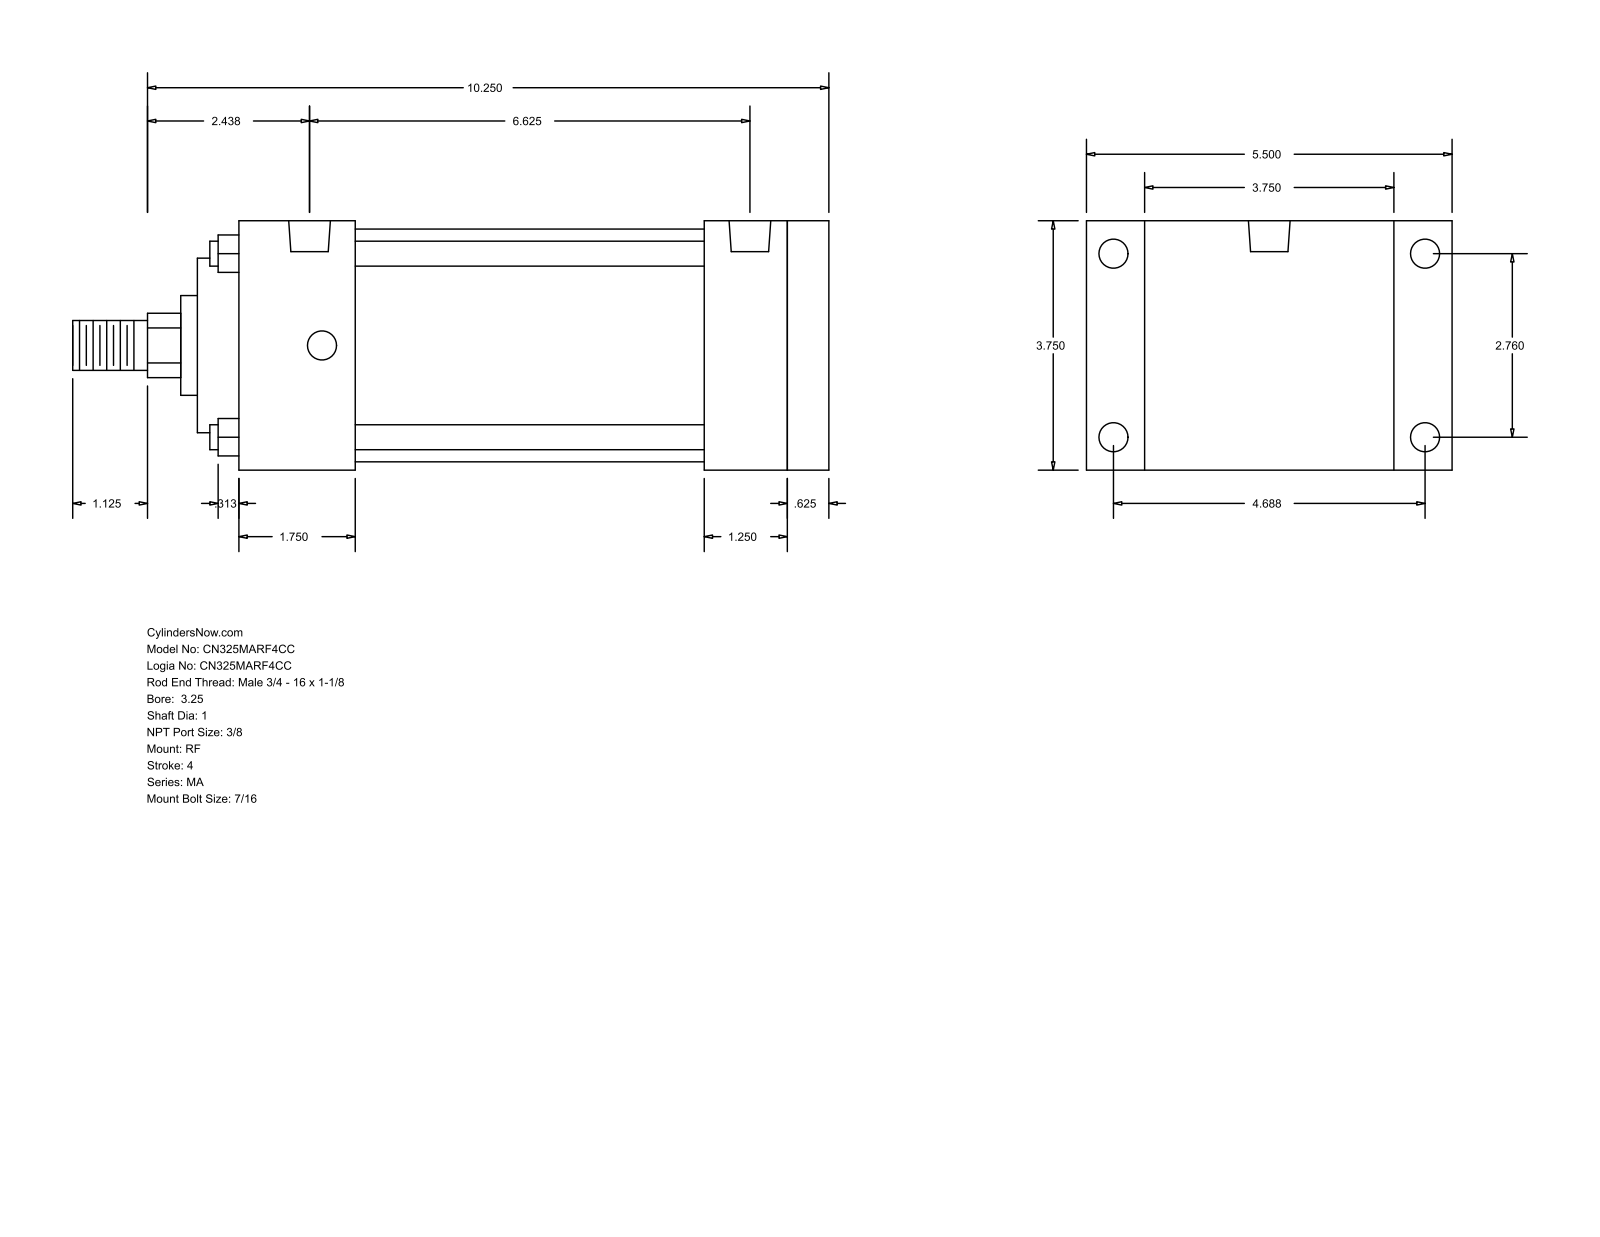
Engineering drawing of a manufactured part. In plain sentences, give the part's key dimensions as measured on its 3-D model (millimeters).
The part is named "MA_RF__0325_1". Its 3-D file was written by "GSSL Pune (CONFIG_CONTROL_DESIGN)". It is 0 solids with 94 faces: 65 planar, 29 cylindrical and 0 other. Overall it measures 288.93 by 139.7 by 95.25 millimeters. Round holes: 8 of diameter 11.11, 2 of diameter 15.93. Round bosses or shafts: 4 of diameter 9.53, 1 of diameter 88.9, 1 of diameter 66.67, 1 of diameter 38.1, 1 of diameter 25.4, 1 of diameter 19.05. Partial cylindrical surfaces (rounded edges, fillets, slot ends): 1 of radius 12.29. The main face-to-face distances are 95.24, 225.43, 209.55, 15.88, 22.23, 117.47, 177.8, 31.75, 47.63, 44.46. The hole center spacings are 4.76, 70.1, 119.06, 138.16, 158.76, 163.52, 168.28.
